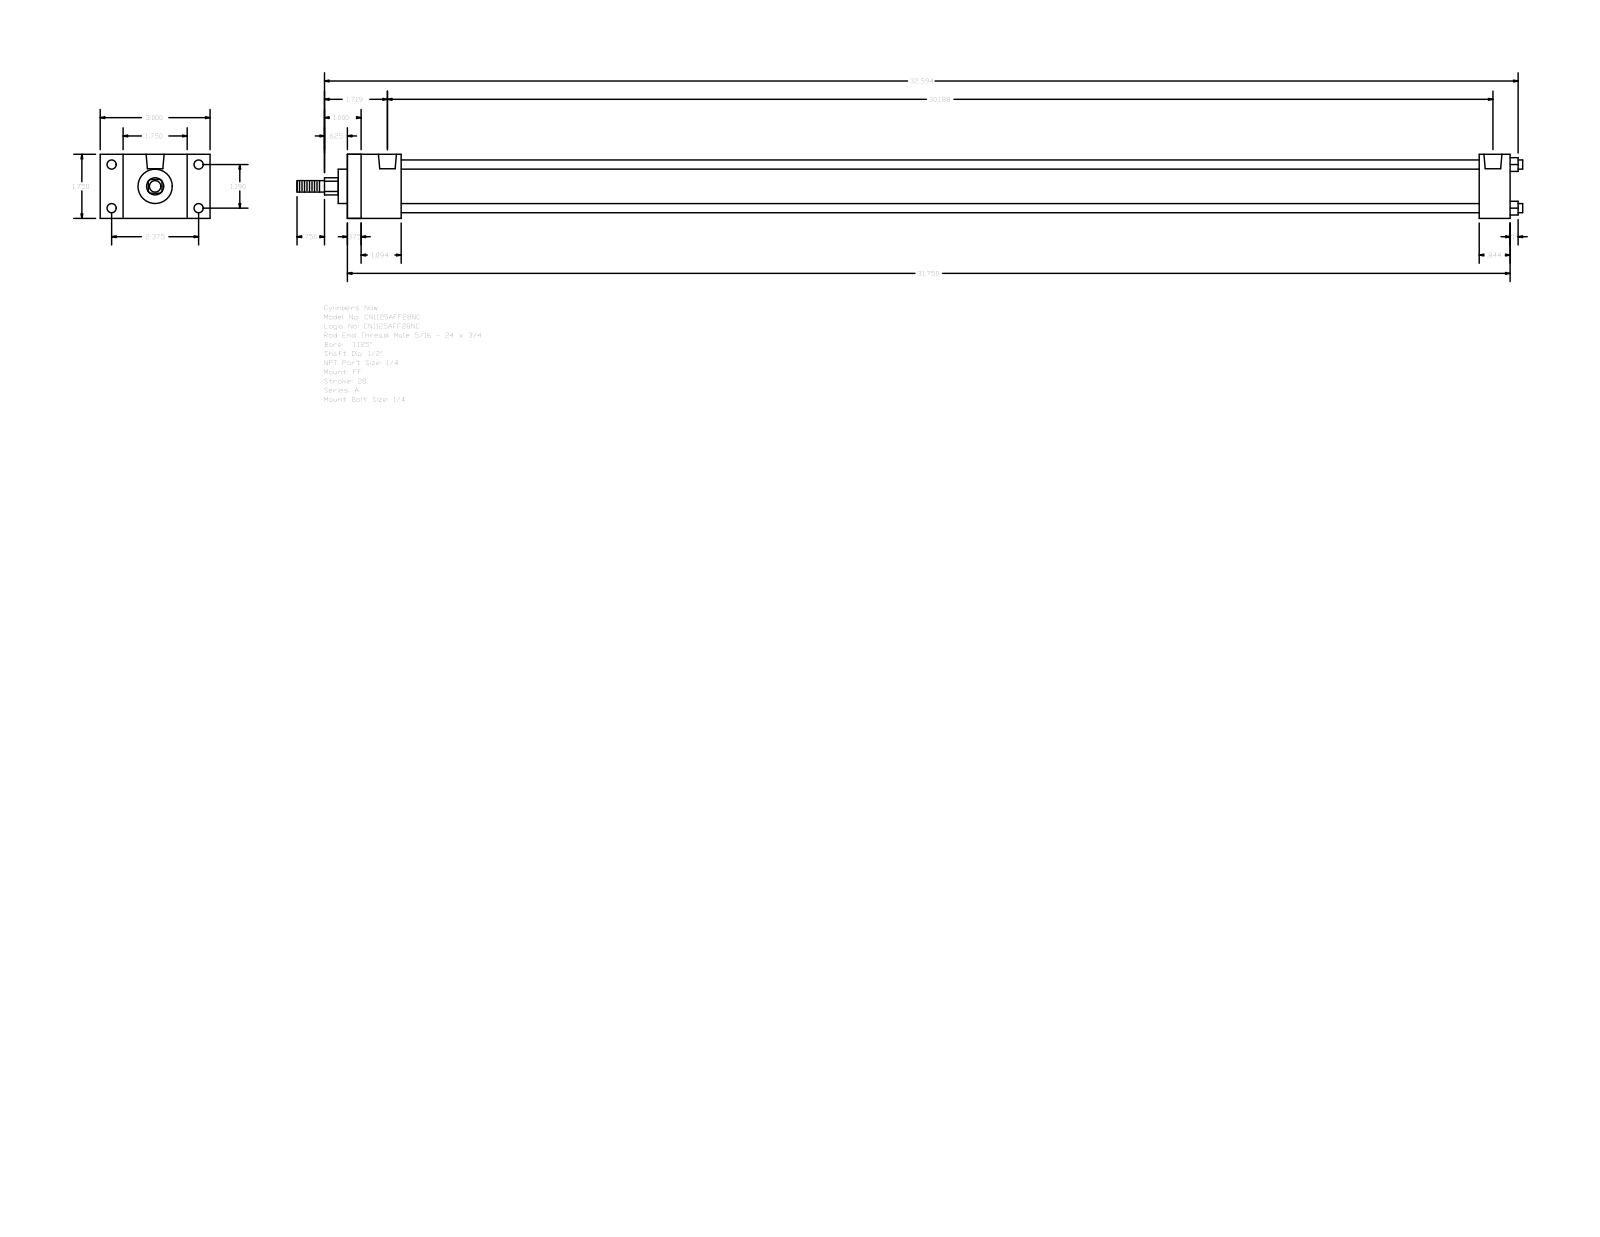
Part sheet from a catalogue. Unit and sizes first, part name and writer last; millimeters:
Units: millimetres
Overall size (bounding box): 850.11 × 76.2 × 44.45
Round holes (diameter × count): ⌀5.56 ×4, ⌀6.35 ×4, ⌀12.49 ×2
Round bosses / shafts (diameter × count): ⌀6.35 ×4, ⌀31.88 ×1, ⌀23.81 ×1, ⌀12.7 ×1, ⌀7.94 ×1
Partial cylindrical surfaces — rounded edges, fillets, slot ends (radius × count): R5.94 ×1
Main face-to-face distances: 44.46, 806.45, 9.52, 796.93, 15.87, 785.01, 775.49, 21.44, 37.3, 27.78
Hole centre spacings: 30.22, 60.32, 67.47, 763.59, 1.58, 1.59, 765.17, 765.18
Bodies: 0 solids, 92 faces (64 planar, 28 cylindrical, 0 other)
Part name (STEP PRODUCT): A_FF__0112_0.5
STEP written by: GSSL Pune (CONFIG_CONTROL_DESIGN)
